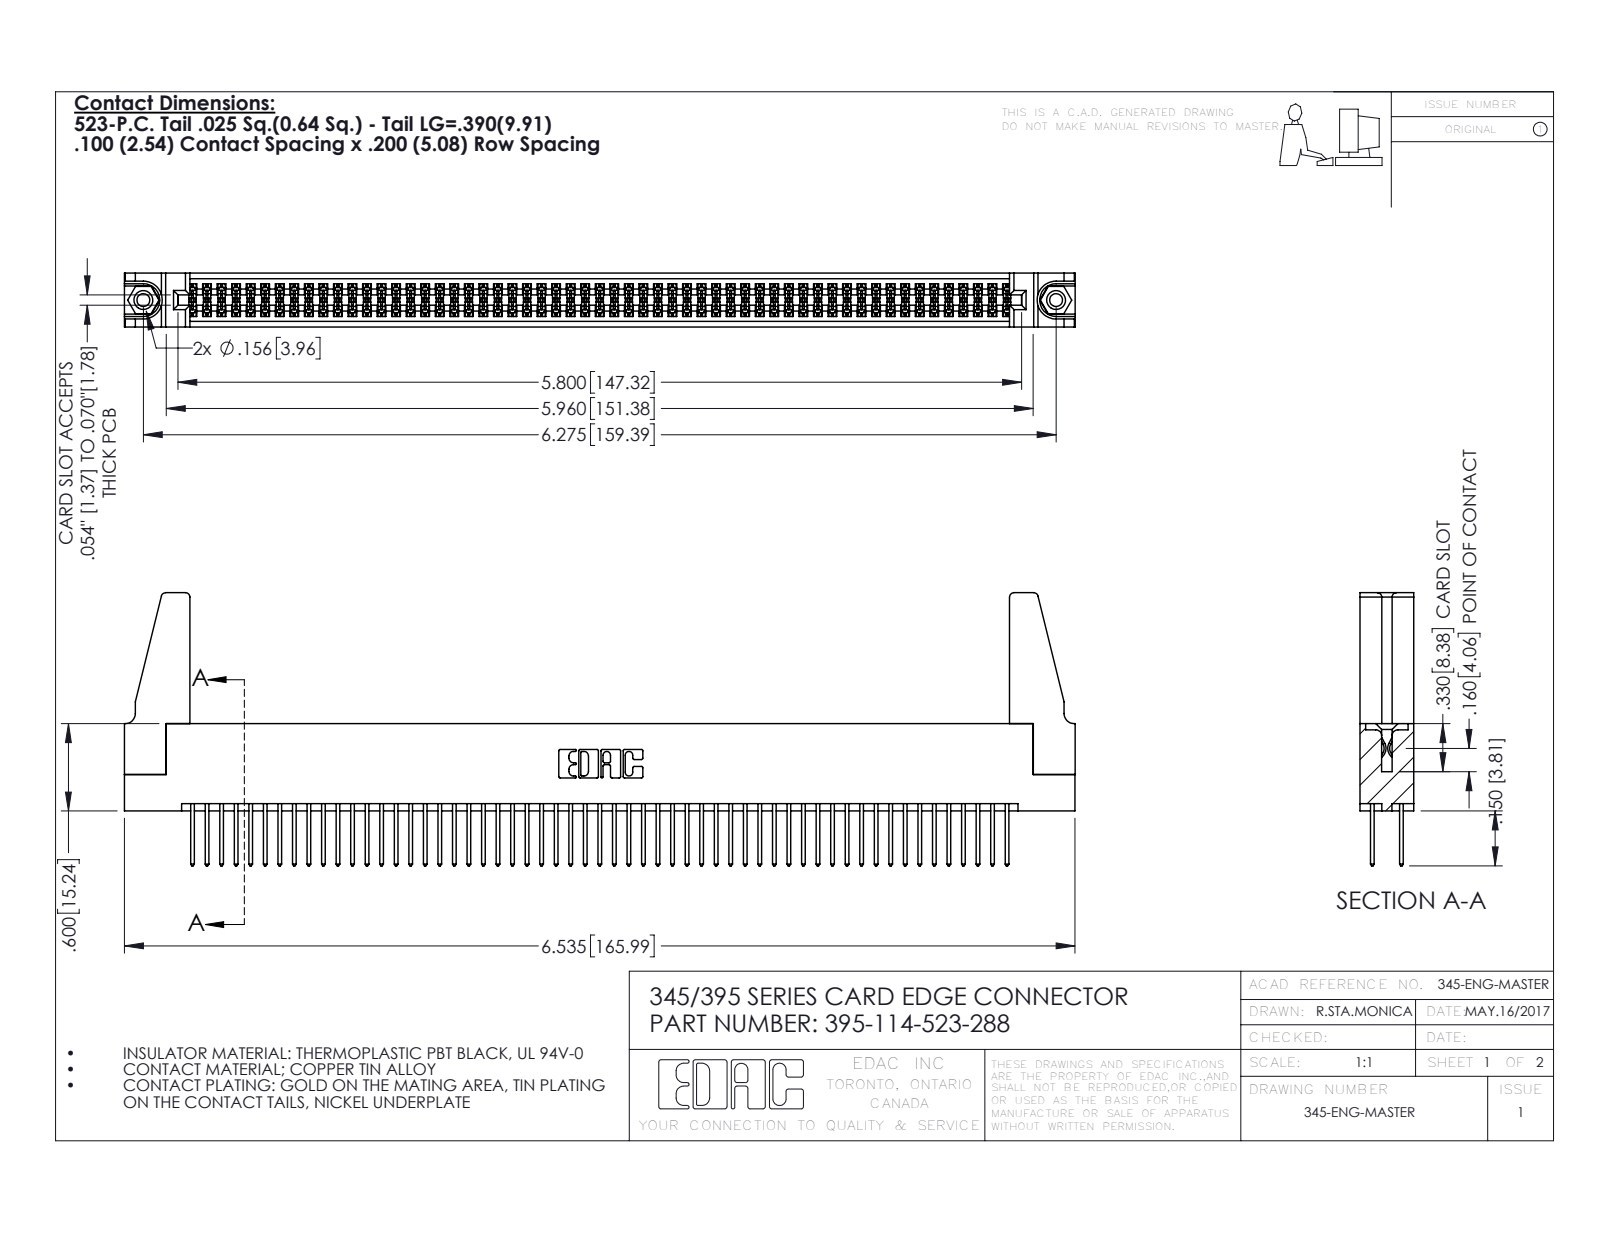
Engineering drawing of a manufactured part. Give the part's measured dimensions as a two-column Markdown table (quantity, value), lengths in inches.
| quantity | value |
| --- | --- |
| part name | 345 Part_Flush Mounting Lugs - 0.156 Dia-TH; 345-292-001_345-293-123; 395-114-523-288; 345-220-078_345-220-088 (+1 more) |
| STEP written by | SolidWorks 2016 (CONFIG_CONTROL_DESIGN) |
| units | inches |
| bodies | 119 solids, 5950 faces (3914 planar, 2020 cylindrical, 16 other) |
| overall size | 6.536 × 1.877 × 0.37 |
| volume | 1.205 in³ |
| surface area | 44.72 in² |
| round holes (diameter × count) | 0.089 × 2, 0.125 × 2, 0.156 × 2, 0.064 × 1 |
| round bosses / shafts (diameter × count) | 0.155 × 2 |
| partial cylindrical surfaces (radius × count) | 0.006 × 171, 0.01 × 114, 0.01 × 22, 0.03 × 8, 0.007 × 6, 0.031 × 6, 0.026 × 3, 0.014 × 2 |
| main face-to-face distances | 0.072, 0.298, 0.2, 0.37, 0.098, 0.272, 0.025, 0.225, 0.175, 0.149 |
| hole center spacings | 0.27, 6.039, 6.275 |
